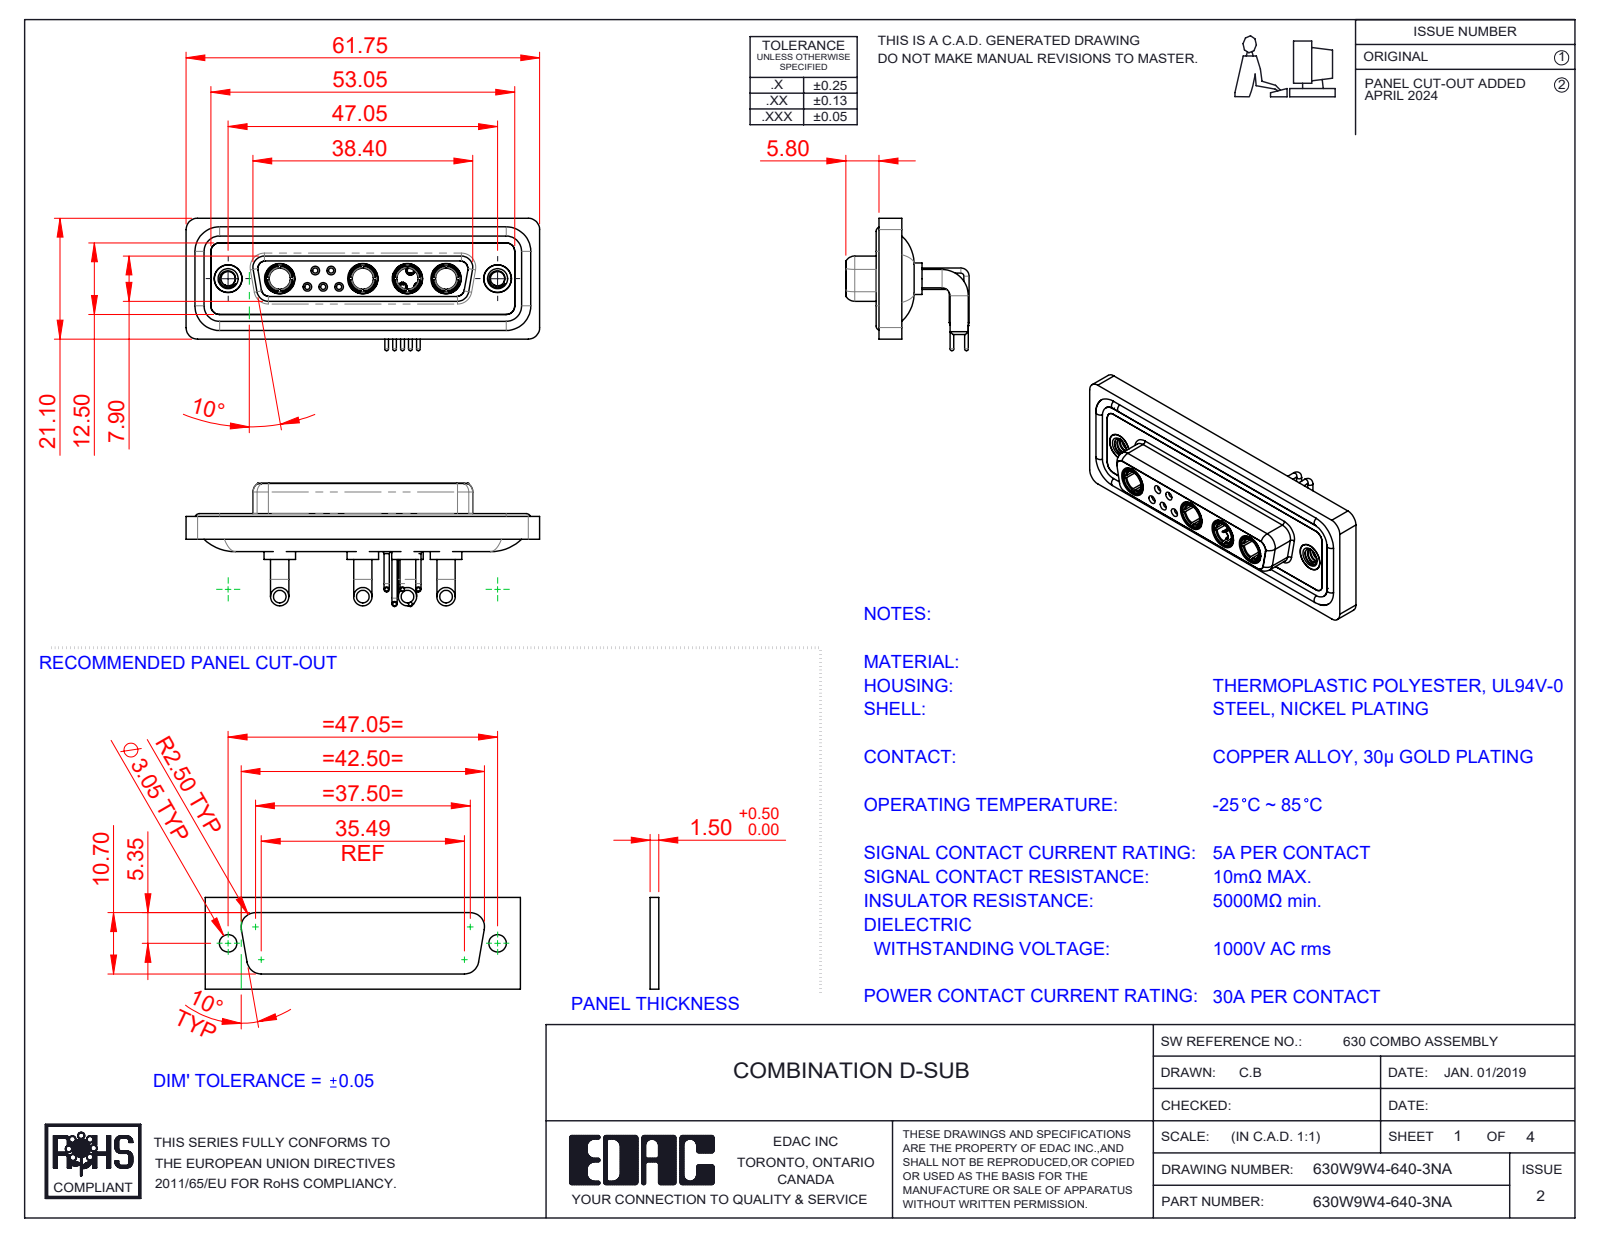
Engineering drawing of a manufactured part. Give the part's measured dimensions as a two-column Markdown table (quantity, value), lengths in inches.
| quantity | value |
| --- | --- |
| part name | 630Combo Contact Row 2_50 Contacts; 630Combo Housing_9W4; 630Combo Contact Row 1_50 Contacts; 630Combo Threaded Rivet_A (+5 more) |
| STEP written by | SolidWorks 2023 (CONFIG_CONTROL_DESIGN) |
| units | inches |
| bodies | 20 solids, 957 faces (296 planar, 401 cylindrical, 260 other) |
| overall size | 2.431 × 0.91 × 0.848 |
| volume | 0.522 in³ |
| surface area | 21.89 in² |
| round holes (diameter × count) | 0.191 × 6, 0.035 × 5, 0.043 × 5, 0.059 × 5, 0.079 × 5, 0.146 × 4, 0.209 × 4, 0.063 × 3, 0.067 × 2, 0.098 × 2, 0.157 × 2, 0.159 × 2 |
| round bosses / shafts (diameter × count) | 0.035 × 10, 0.063 × 9, 0.126 × 8, 0.079 × 5, 0.059 × 5, 0.026 × 5, 0.217 × 4, 0.205 × 4 |
| partial cylindrical surfaces (radius × count) | 0.059 × 18, 0.079 × 18, 0.053 × 8, 0.063 × 8, 0.01 × 4, 0.02 × 4, 0.024 × 4, 0.026 × 4 |
| main face-to-face distances | 0.016, 0.071, 0.161, 0.043, 0.063, 0.059, 0.098, 0.122, 0.146, 0.055 |
| hole center spacings | 0.124, 0.109, 0.198, 0.545, 0.436, 0.504, 0.61, 0.218 |
